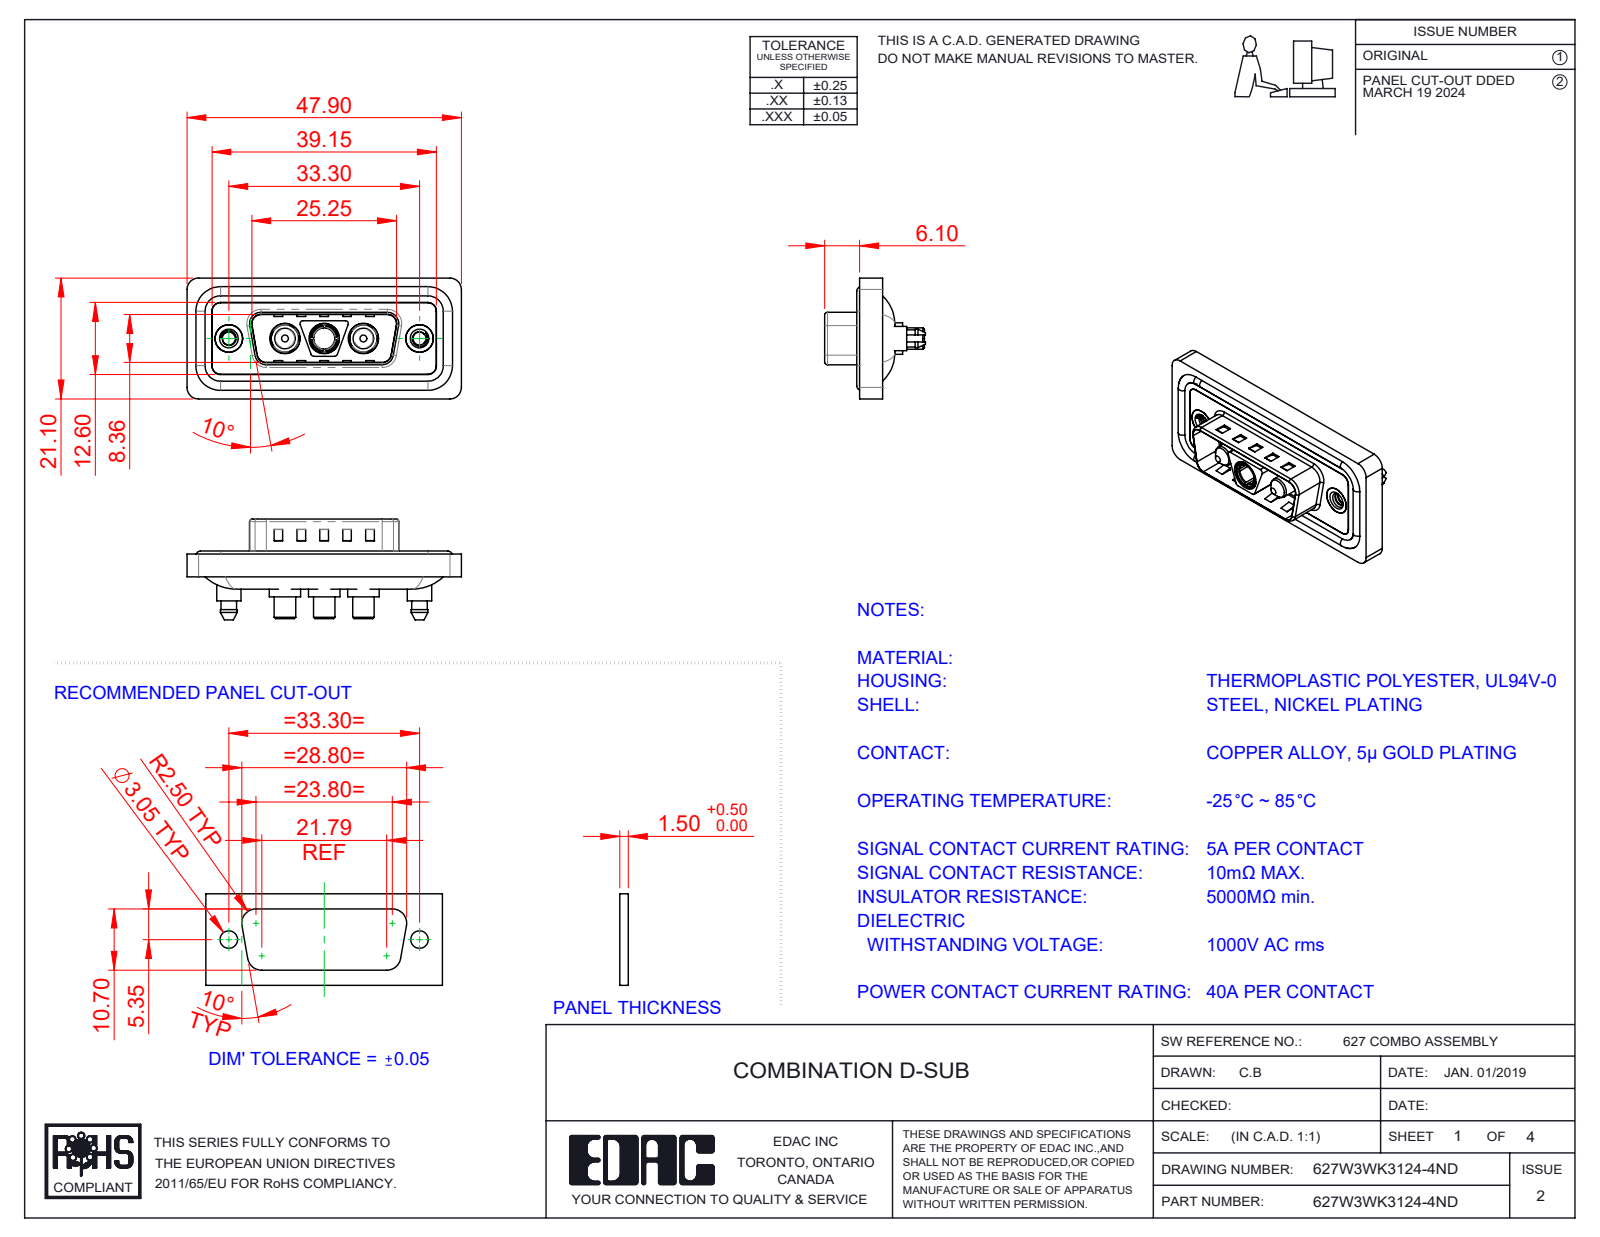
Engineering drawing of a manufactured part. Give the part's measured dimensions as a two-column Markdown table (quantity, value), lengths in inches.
| quantity | value |
| --- | --- |
| part name | 627W3WK3124-4ND; 627Combo Shell Front_15 Contacts; Power Socket_40A S; 627Combo Waterproof Housing_15 Contacts (+5 more) |
| STEP written by | SolidWorks 2023 (CONFIG_CONTROL_DESIGN) |
| units | inches |
| bodies | 13 solids, 667 faces (247 planar, 290 cylindrical, 130 other) |
| overall size | 1.886 × 0.831 × 0.693 |
| volume | 0.359 in³ |
| surface area | 14.72 in² |
| round holes (diameter × count) | 0.191 × 3, 0.209 × 3, 0.089 × 2, 0.157 × 2, 0.189 × 2, 0.197 × 2, 0.146 × 1 |
| round bosses / shafts (diameter × count) | 0.063 × 4, 0.217 × 3, 0.205 × 3, 0.187 × 3, 0.148 × 3, 0.213 × 2, 0.193 × 2, 0.167 × 2 |
| partial cylindrical surfaces (radius × count) | 0.059 × 28, 0.079 × 20, 0.02 × 12, 0.063 × 10, 0.01 × 4, 0.024 × 4, 0.026 × 4, 0.035 × 4 |
| main face-to-face distances | 0.016, 0.043, 0.059, 0.122, 0.02, 0.063, 0.114, 0.157, 0.028, 0.032 |
| hole center spacings | 0.27, 0.386, 0.656, 0.925, 0.539, 1.311 |
